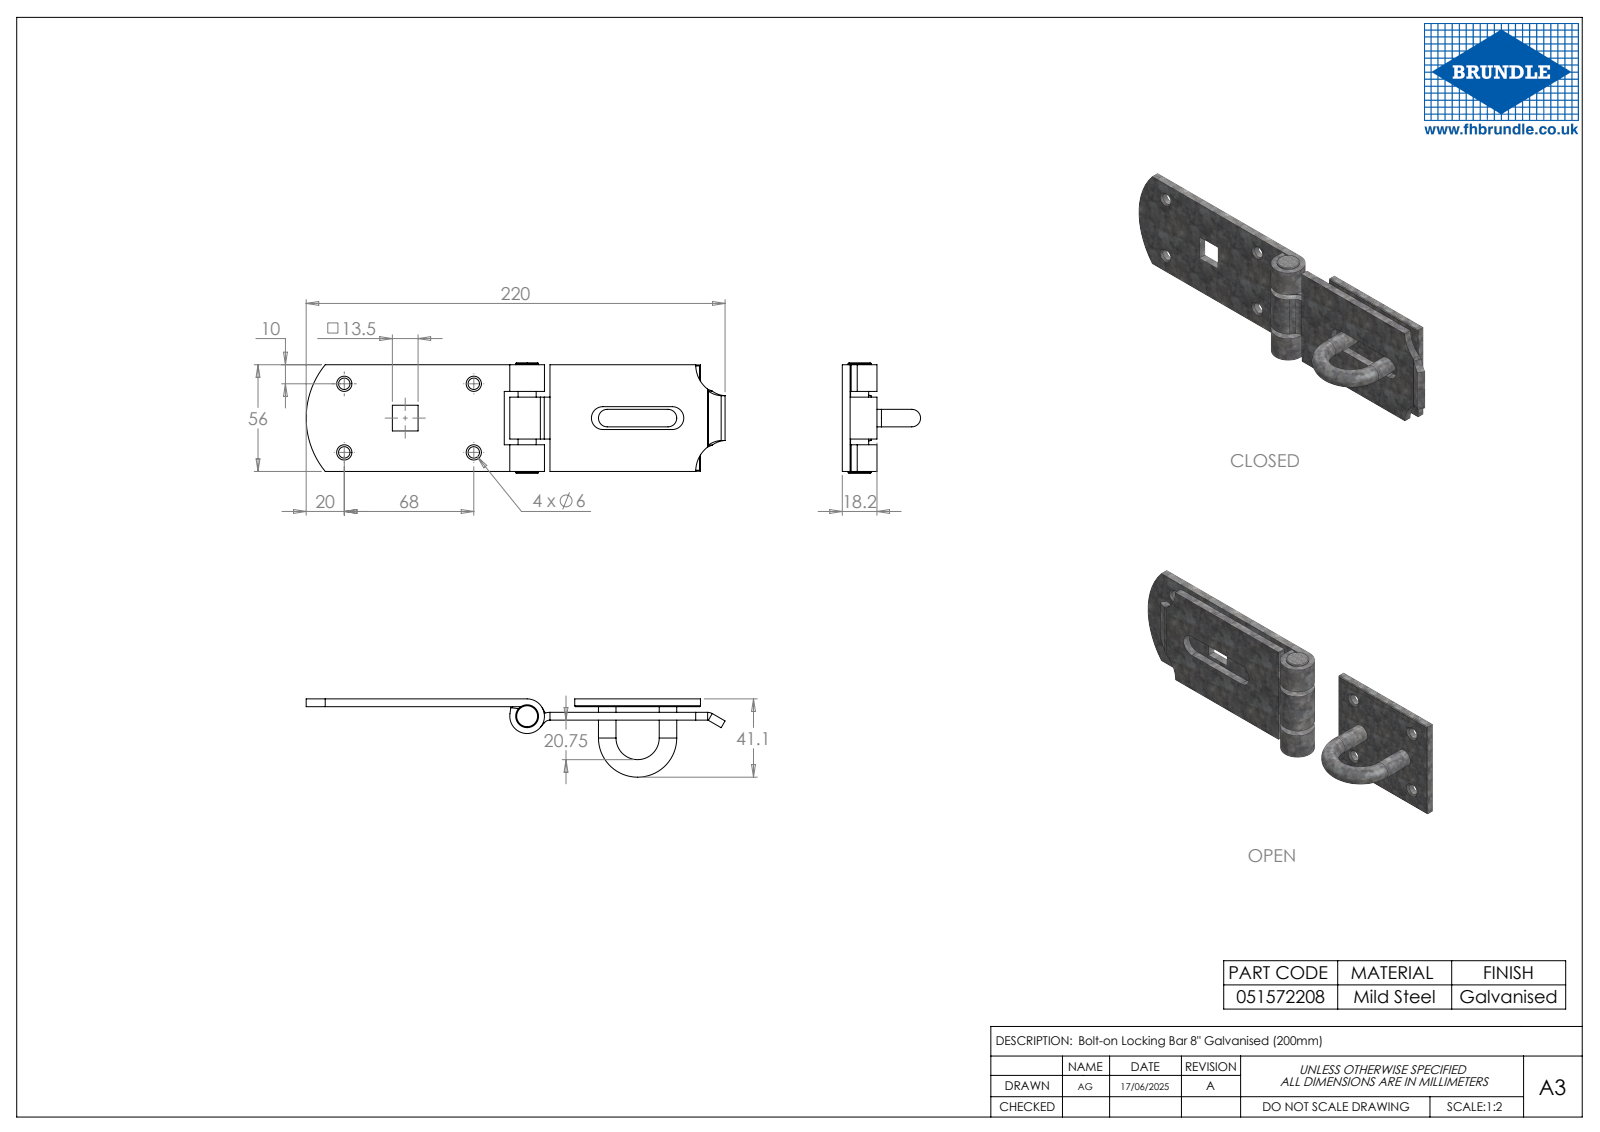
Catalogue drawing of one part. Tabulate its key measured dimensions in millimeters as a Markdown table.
| quantity | value |
| --- | --- |
| part name | 051572208; 051572208 Part3; 051572208 Part1; 051572208 Part4 (+1 more) |
| STEP written by | SolidWorks 2023 (CONFIG_CONTROL_DESIGN) |
| units | millimeters |
| bodies | 5 solids, 125 faces (46 planar, 55 cylindrical, 24 other) |
| overall size | 219.92 × 58 × 41.1 |
| volume | 73 381 mm³ |
| surface area | 41 309 mm² |
| round holes (diameter × count) | 5.8 × 4, 6 × 4, 10 × 1 |
| round bosses / shafts (diameter × count) | 9.2 × 2, 18.2 × 1, 12 × 1, 9.5 × 1 |
| partial cylindrical surfaces (radius × count) | 0.5 × 4, 16.27 × 4, 6 × 2, 0.74 × 1, 4 × 1, 4.84 × 1, 8 × 1, 44.2 × 1 |
| main face-to-face distances | 4.1, 7.05, 11.15, 2.95, 56, 17, 22, 55.88, 14, 42 |
| hole center spacings | 35.96, 36, 43.2, 56.21, 64.4, 68, 73.77, 76.94 |
